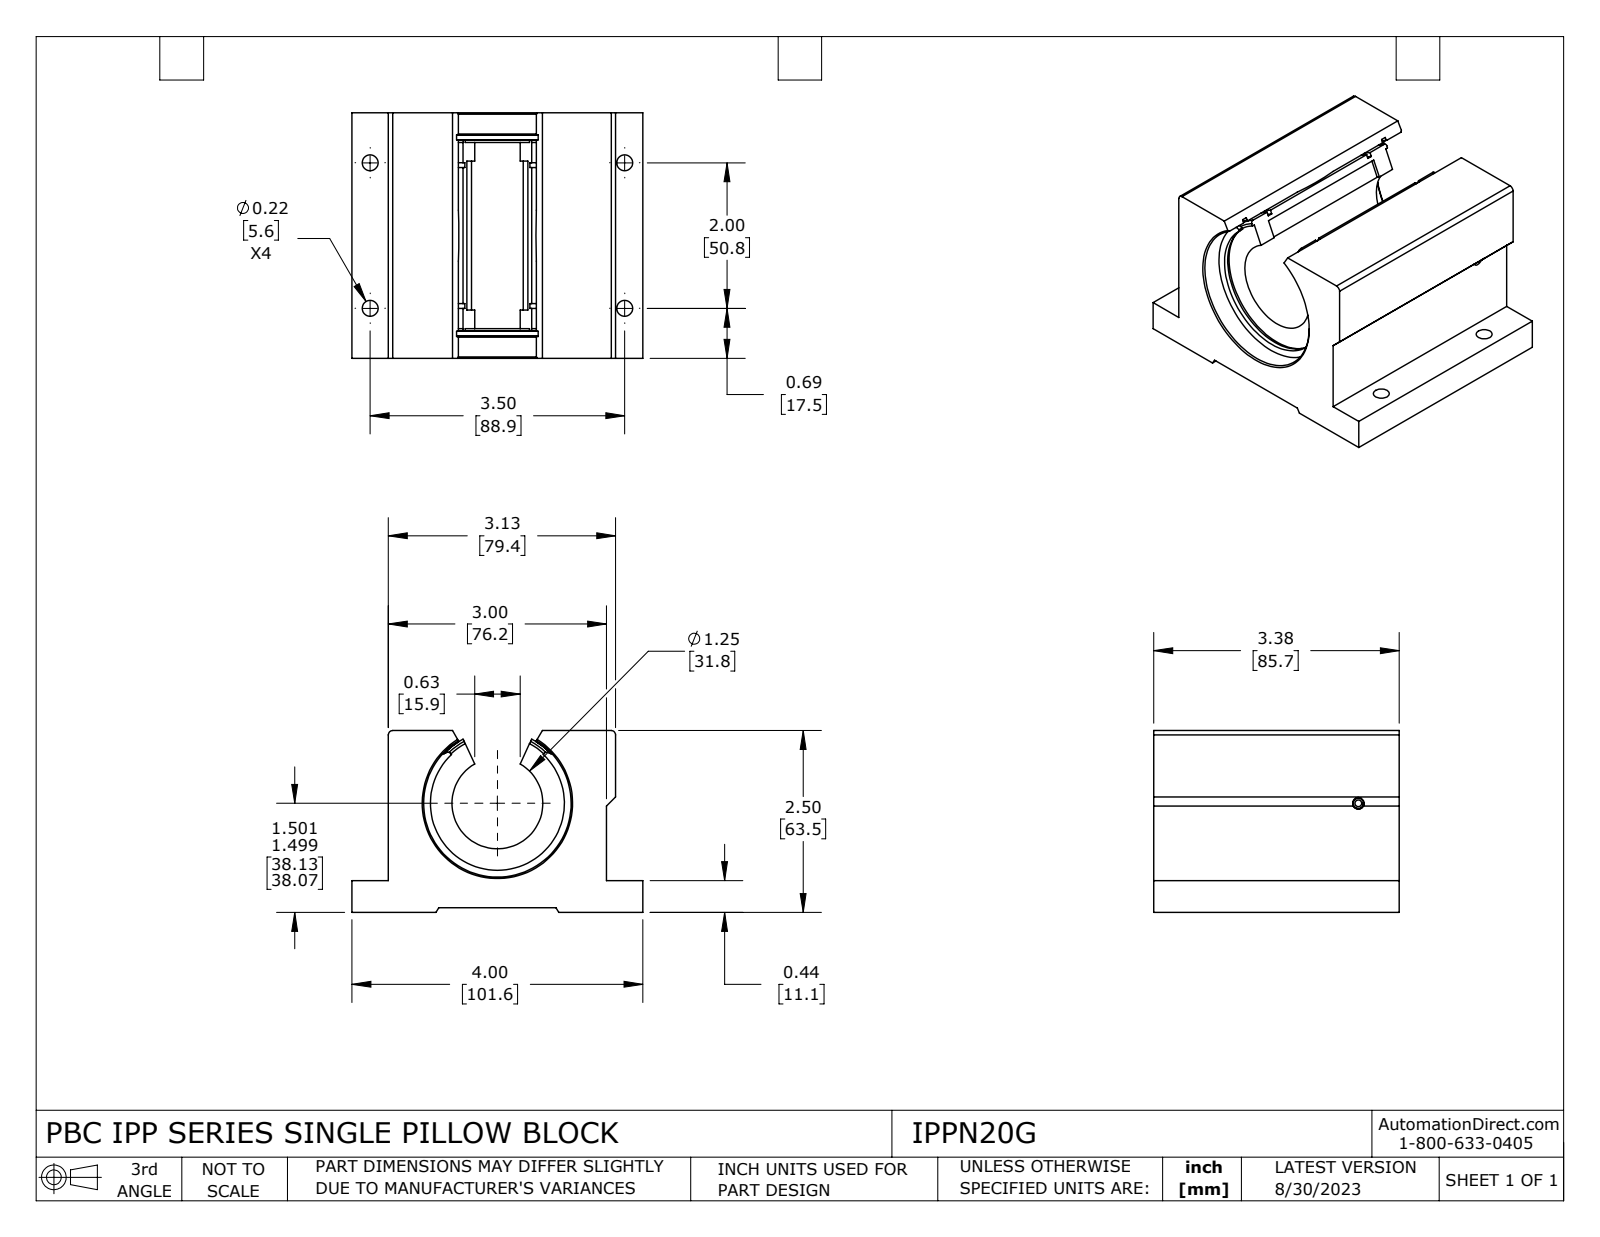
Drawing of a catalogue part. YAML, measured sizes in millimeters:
part_name: "IPPN20G"
step_written_by: "SolidWorks 2021 (CONFIG_CONTROL_DESIGN)"
units: millimeters
bodies: {solids: 5, faces: 157, planar: 52, cylindrical: 74, other: 31}
overall_size: [101.6, 85.7, 63.5]
volume: 324800
surface_area: 67100
round_holes:
  - {diameter: 5.6, count: 4}
  - {diameter: 2.3, count: 1}
  - {diameter: 4, count: 1}
  - {diameter: 5.1, count: 1}
  - {diameter: 31.8, count: 1}
  - {diameter: 47.3, count: 1}
  - {diameter: 51.5, count: 1}
  - {diameter: 53.9, count: 1}
round_bosses_or_shafts:
  - {diameter: 50.8, count: 1}
  - {diameter: 47.9, count: 1}
  - {diameter: 4, count: 1}
partial_cylinders:
  - {radius: 1.3, count: 2}
  - {radius: 1.5, count: 2}
  - {radius: 4.6, count: 2}
  - {radius: 22.3, count: 1}
  - {radius: 23.4, count: 1}
  - {radius: 27.4, count: 1}
face_to_face_distances: [63.5, 1.7, 61.8, 85.7, 76.2, 11.1, 9.4, 52.4, 12.7, 88.9]
hole_center_spacings: [50.8, 88.9, 102.4]
